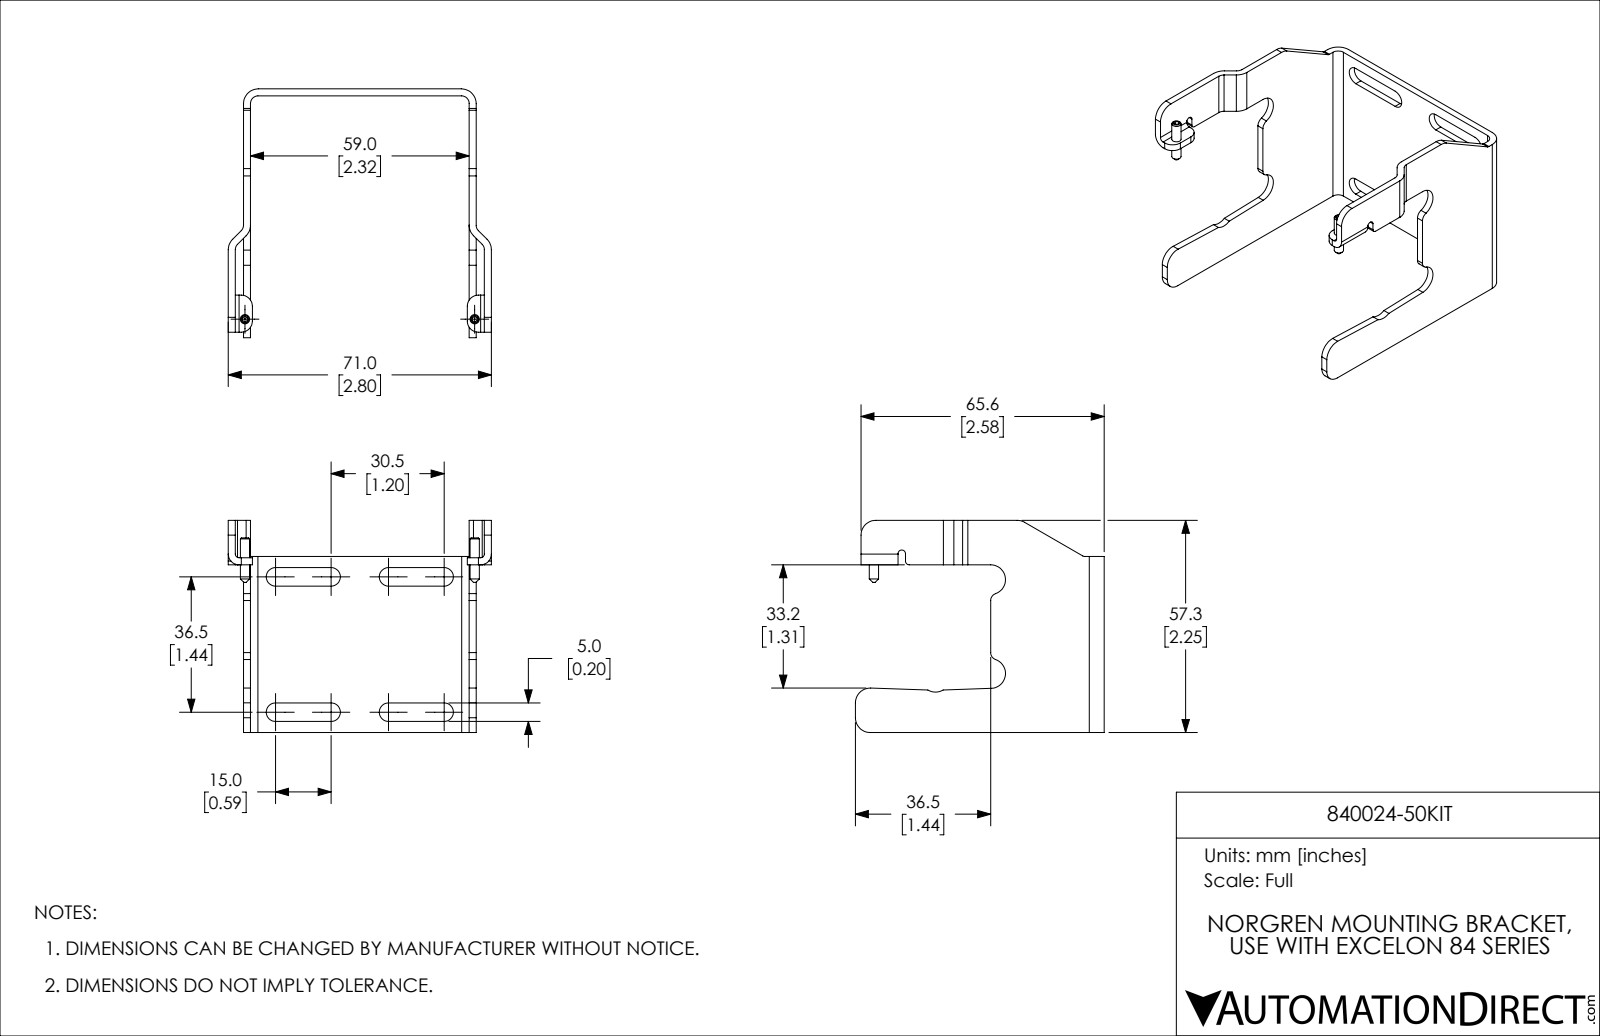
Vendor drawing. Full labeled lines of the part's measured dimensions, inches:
Part name (STEP PRODUCT): 840024-50KIT
STEP written by: SolidWorks 2021 (CONFIG_CONTROL_DESIGN)
Units: inches
Bodies: 1 solid, 144 faces (68 planar, 68 cylindrical, 8 other)
Overall size (bounding box): 2.795 × 2.643 × 2.254
Volume: 0.838 in³ · Surface area: 25.08 in²
Round bosses / shafts (diameter × count): ⌀0.098 ×2
Partial cylindrical surfaces — rounded edges, fillets, slot ends (radius × count): R0.157 ×13, R0.079 ×8, R0.098 ×8, R0.039 ×5, R0.118 ×4, R0.114 ×2
Main face-to-face distances: 0.075, 2.398, 2.323, 2.472, 0.161, 2.559, 0.087, 2.484, 0.236, 2.634
